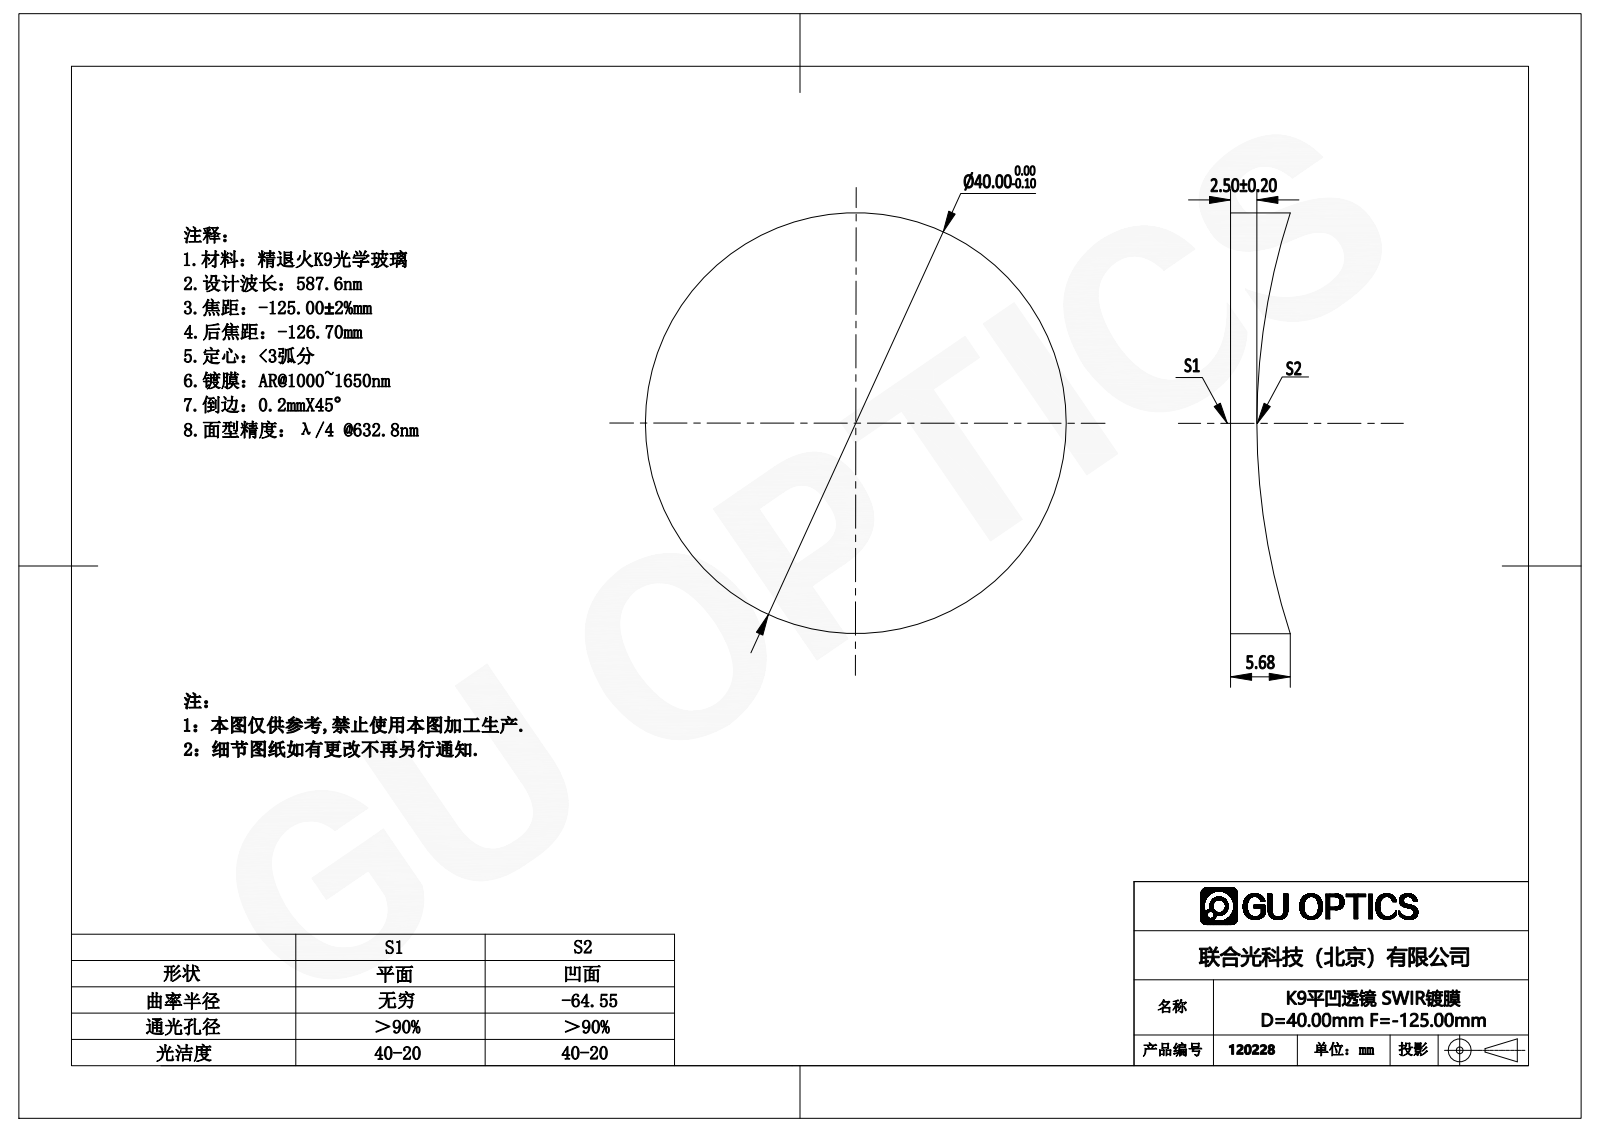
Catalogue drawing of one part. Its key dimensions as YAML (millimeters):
part_name: "12016"
step_written_by: "SolidWorks 2016 (AUTOMOTIVE_DESIGN)"
units: millimeters
bodies: {solids: 1, faces: 5, planar: 1, cylindrical: 2, other: 2}
overall_size: [40, 40, 5.68]
volume: 5121
surface_area: 3258
round_bosses_or_shafts:
  - {diameter: 40, count: 1}
